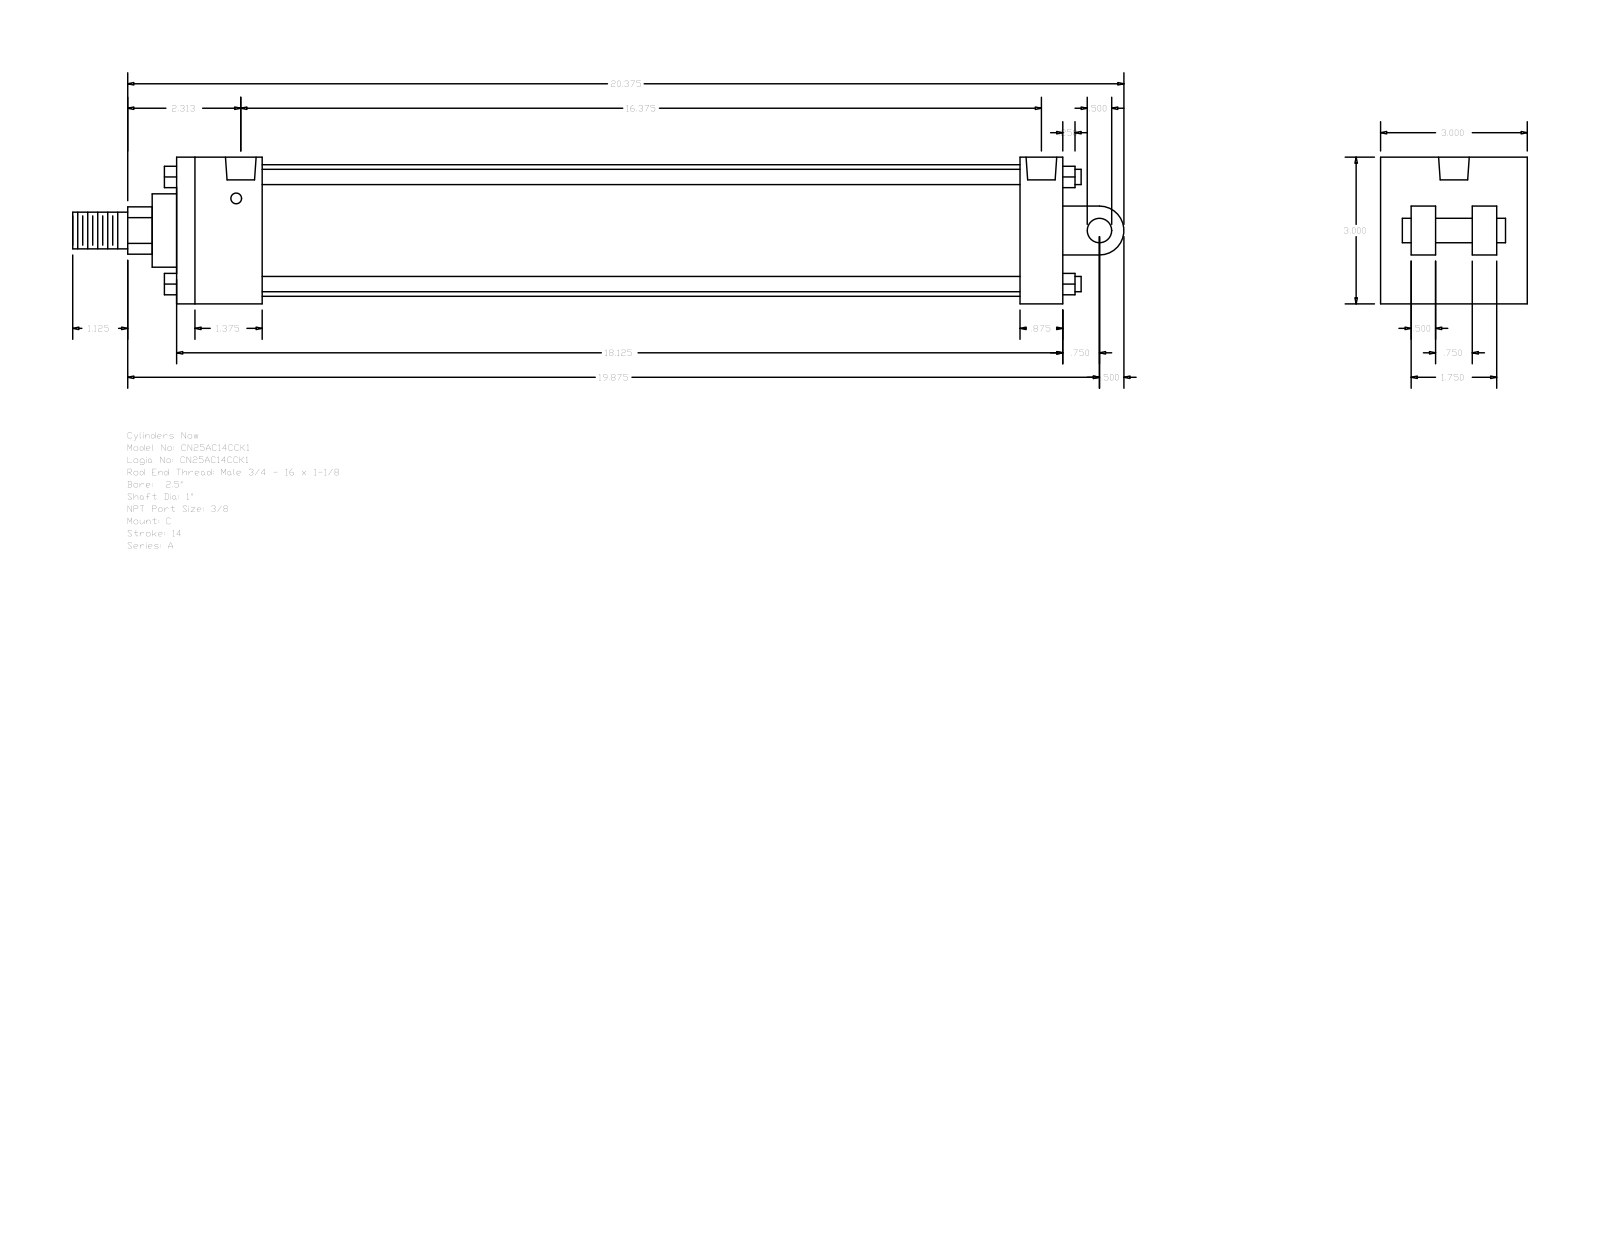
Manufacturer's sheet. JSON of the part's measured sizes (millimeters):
{"part_name": "A_C__0250_1", "step_written_by": "GSSL Pune (CONFIG_CONTROL_DESIGN)", "units": "millimeters", "bodies": {"solids": 0, "faces": 135, "planar": 102, "cylindrical": 33, "other": 0}, "overall_size": [546.1, 76.2, 76.2], "round_holes": [[5.56, 4], [15.93, 2]], "round_bosses_or_shafts": [[7.94, 4], [68.33, 1], [38.1, 1], [25.4, 1], [19.05, 1], [12.7, 1]], "partial_cylinders_radius": [[12.29, 1], [12.7, 1]], "face_to_face_distances": [76.2, 460.37, 12.7, 44.45, 438.15, 393.7, 415.92, 22.22, 15.87, 25.4], "hole_center_spacings": [2.38, 418.3, 420.68, 415.92]}
